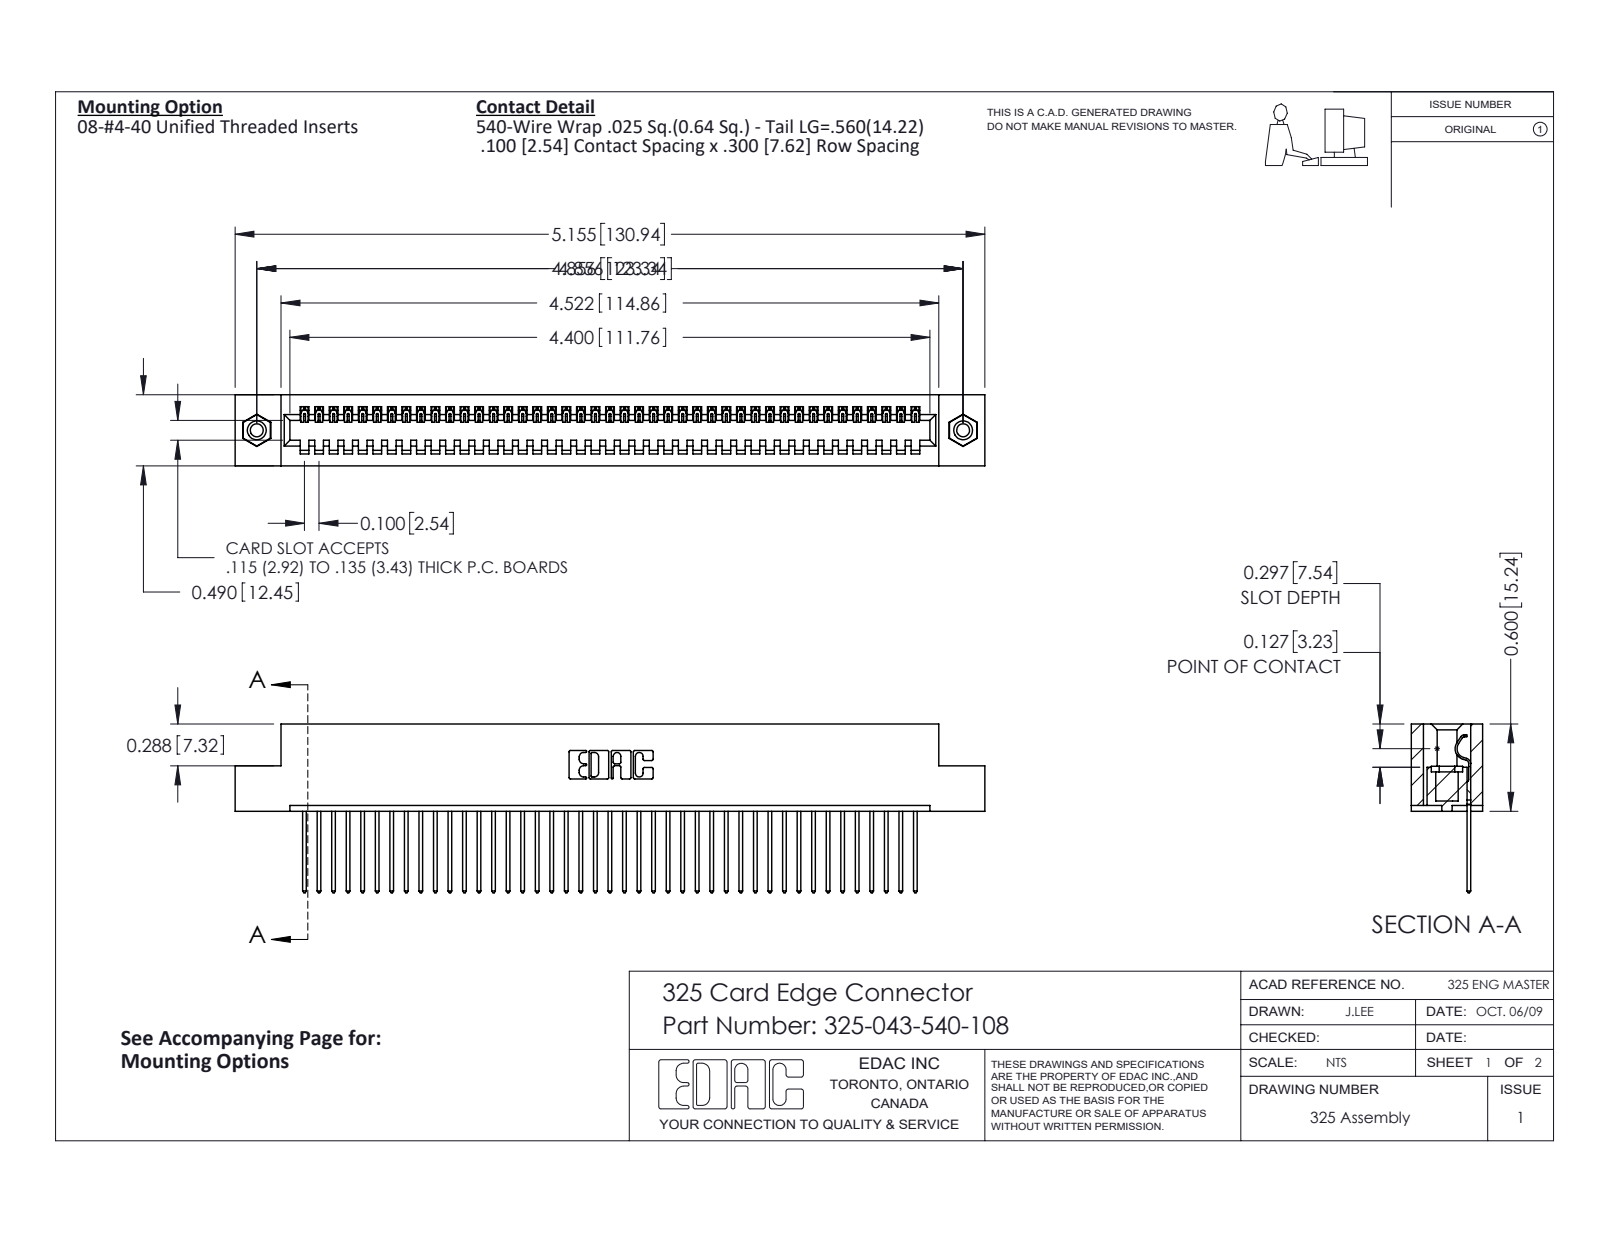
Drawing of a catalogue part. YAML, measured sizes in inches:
part_name: "325-292-001_325-293-140; 325 Part_TI; 325-043-540-108; 345-250-001_345-250-003-102"
step_written_by: "SolidWorks 2016 (CONFIG_CONTROL_DESIGN)"
units: inches
bodies: {solids: 46, faces: 2668, planar: 1908, cylindrical: 744, other: 16}
overall_size: [5.155, 1.16, 0.49]
volume: 1.018
surface_area: 28.97
round_holes:
  - {diameter: 0.089, count: 2}
  - {diameter: 0.125, count: 2}
  - {diameter: 0.16, count: 2}
round_bosses_or_shafts:
  - {diameter: 0.155, count: 2}
partial_cylinders:
  - {radius: 0.006, count: 86}
  - {radius: 0.01, count: 86}
  - {radius: 0.01, count: 22}
  - {radius: 0.007, count: 6}
  - {radius: 0.031, count: 6}
  - {radius: 0.026, count: 3}
  - {radius: 0.014, count: 1}
  - {radius: 0.022, count: 1}
face_to_face_distances: [0.083, 0.407, 0.49, 0.3, 0.107, 0.383, 0.025, 0.325, 0.56, 0.04]
hole_center_spacings: [4.856]
